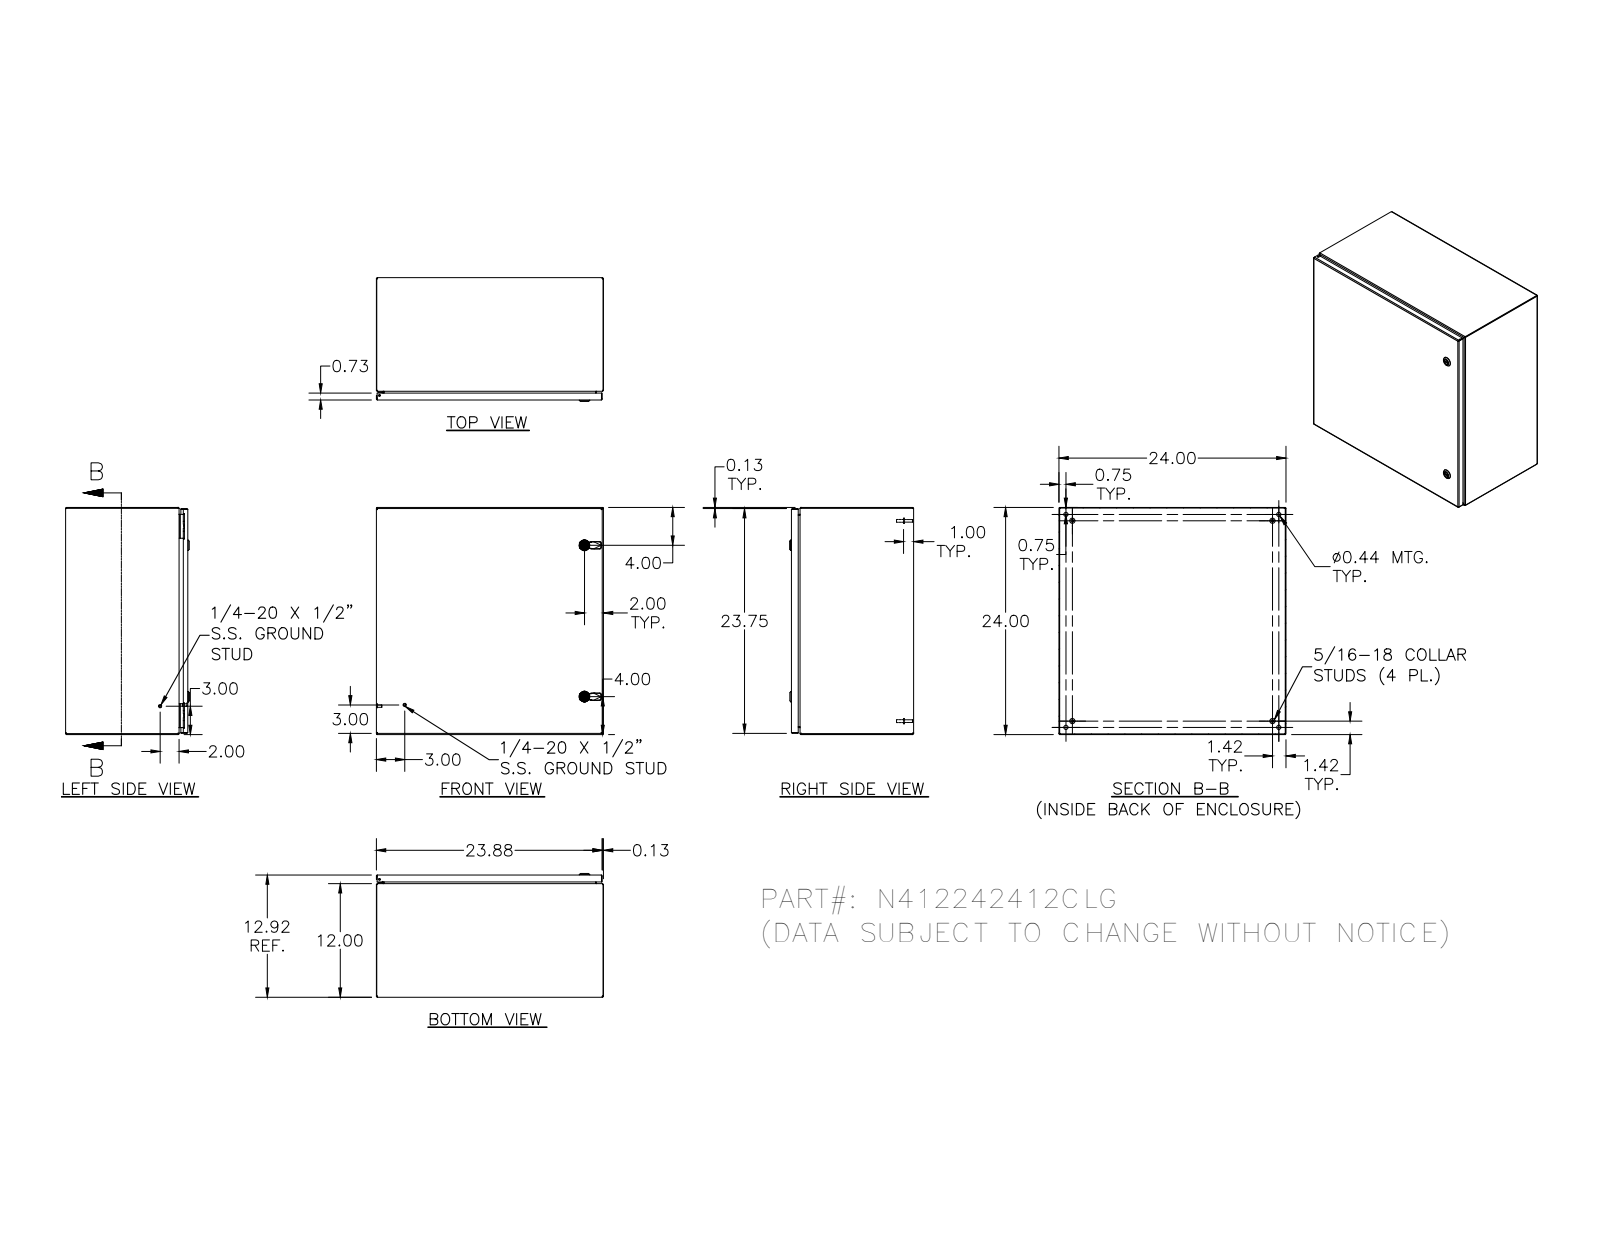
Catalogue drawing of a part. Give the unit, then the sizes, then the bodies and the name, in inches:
Units: inches
Overall size (bounding box): 24 × 24 × 13.075
Round holes (diameter × count): ⌀0.188 ×5, ⌀0.093 ×4, ⌀0.152 ×4, ⌀0.167 ×4, ⌀0.172 ×4, ⌀0.437 ×4, ⌀0.156 ×2, ⌀0.197 ×2, ⌀0.315 ×2, ⌀0.394 ×2, ⌀0.402 ×2, ⌀0.634 ×2
Round bosses / shafts (diameter × count): ⌀0.25 ×10, ⌀0.563 ×4, ⌀0.36 ×4, ⌀0.32 ×4, ⌀0.3 ×4, ⌀0.256 ×4, ⌀0.164 ×4, ⌀0.131 ×4
Partial cylindrical surfaces — rounded edges, fillets, slot ends (radius × count): R0.012 ×54, R0.031 ×30, R0.05 ×26, R0.02 ×23, R0.105 ×20, R0.016 ×18, R0.125 ×16, R0.032 ×8
Main face-to-face distances: 0.074, 12.843, 0.074, 23.926, 23.852, 23.926, 24, 12.769, 12.917, 0.917
Hole centre spacings: 20, 0.66, 22.5, 0.656, 1.307, 1.965, 22.869, 0.5
Volume: 185.2 in³ · Surface area: 5 025 in²
Bodies: 40 solids, 1812 faces (704 planar, 676 cylindrical, 432 other)
Part name (STEP PRODUCT): N412242412CLG
STEP written by: SolidWorks 2018 (AUTOMOTIVE_DESIGN)
